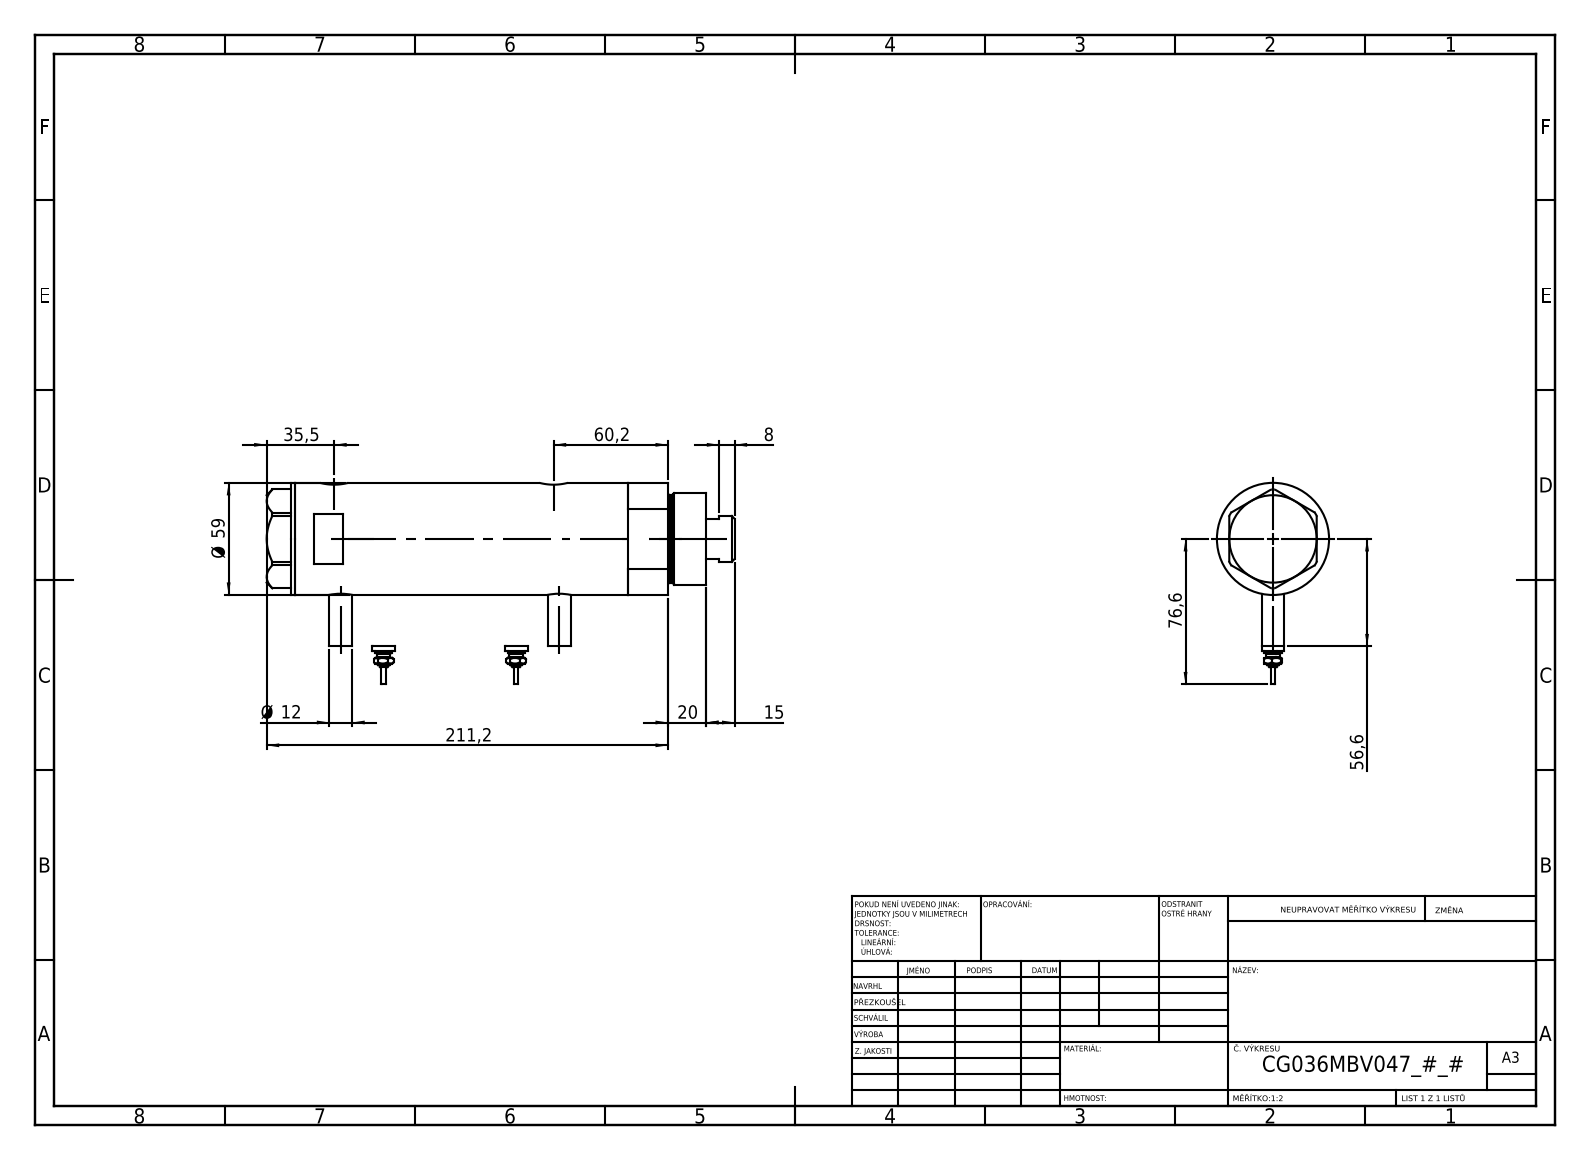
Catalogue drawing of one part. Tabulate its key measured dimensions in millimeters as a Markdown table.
| quantity | value |
| --- | --- |
| part name | V270CG_MIDDLE; Switch; V270CG_VC; V270CG_BACK (+1 more) |
| STEP written by | SolidWorks 2019 (CONFIG_CONTROL_DESIGN) |
| units | millimeters |
| bodies | 6 solids, 212 faces (79 planar, 69 cylindrical, 64 other) |
| overall size | 246.2 × 106.1 × 59 |
| volume | 581 728 mm³ |
| surface area | 117 261 mm² |
| round holes (diameter × count) | 9.73 × 2, 12.5 × 2, 15 × 2, 8.5 × 1, 25 × 1, 26.5 × 1, 36 × 1, 40 × 1, 52 × 1 |
| round bosses / shafts (diameter × count) | 12 × 4, 9 × 2, 7 × 2, 4.5 × 2, 2.5 × 2, 59 × 1, 48 × 1, 46 × 1 |
| main face-to-face distances | 137.2, 23.5, 113.7, 15, 38.5, 152.2, 2, 231.2, 216.2, 192.7 |
| hole center spacings | 2.9, 3.5, 112, 114.9, 115.5, 118.4 |
